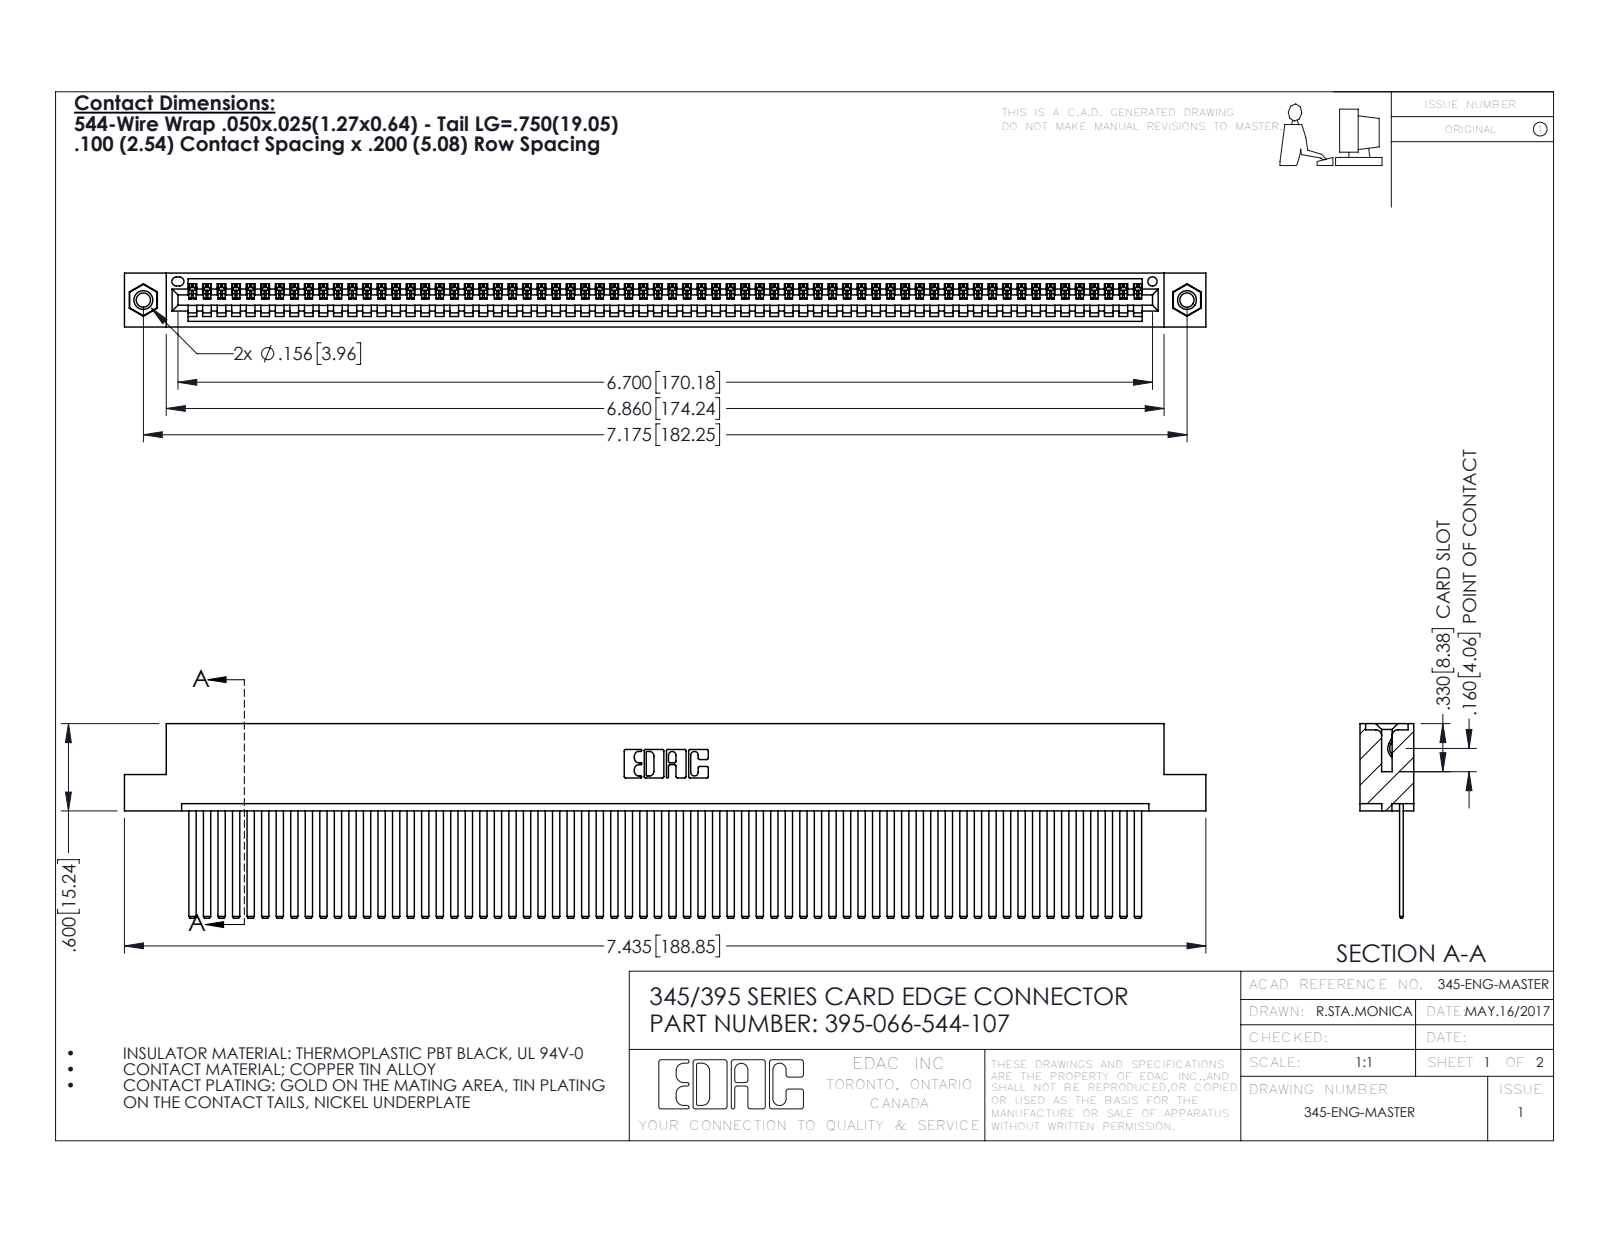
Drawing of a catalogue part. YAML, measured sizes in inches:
part_name: "395-066-544-107; 345-292-001_345-293-144; 345 Part_Flush Mounting Lugs - 0.156 Dia-TI; 345-250-001_345-250-005-103"
step_written_by: "SolidWorks 2016 (CONFIG_CONTROL_DESIGN)"
units: inches
bodies: {solids: 69, faces: 3618, planar: 2488, cylindrical: 1114, other: 16}
overall_size: [7.435, 1.337, 0.37]
volume: 1.152
surface_area: 43.01
round_holes:
  - {diameter: 0.098, count: 2}
  - {diameter: 0.125, count: 2}
  - {diameter: 0.156, count: 2}
  - {diameter: 0.064, count: 1}
round_bosses_or_shafts:
  - {diameter: 0.155, count: 2}
partial_cylinders:
  - {radius: 0.006, count: 132}
  - {radius: 0.01, count: 22}
  - {radius: 0.007, count: 6}
  - {radius: 0.031, count: 6}
  - {radius: 0.026, count: 3}
  - {radius: 0.031, count: 2}
  - {radius: 0.04, count: 2}
  - {radius: 0.014, count: 1}
face_to_face_distances: [0.072, 0.298, 0.025, 0.098, 0.272, 0.37, 0.2, 0.225, 0.149, 0.072]
hole_center_spacings: [0.27, 6.939, 7.175]
